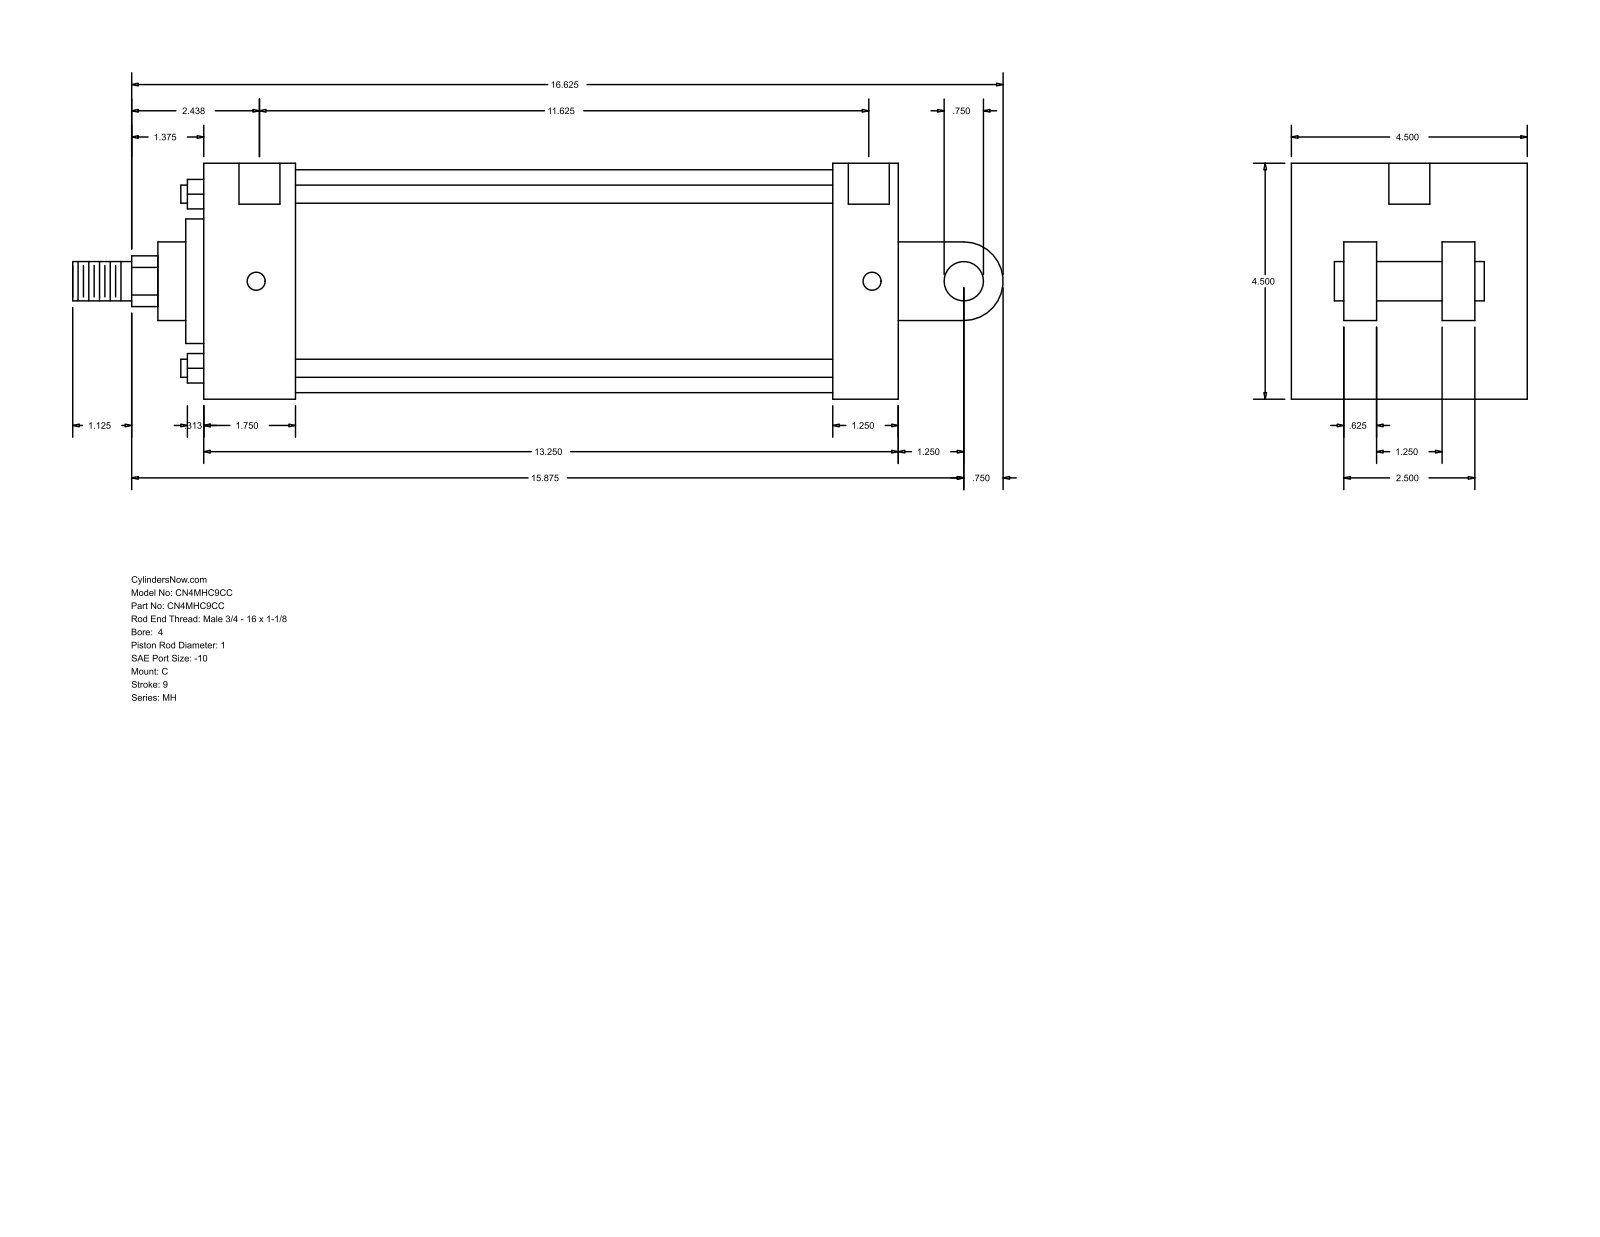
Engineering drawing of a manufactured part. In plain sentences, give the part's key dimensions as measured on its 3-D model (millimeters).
The part is named "MH_C__0400_1". Its 3-D file was written by "GSSL Pune (CONFIG_CONTROL_DESIGN)". It is 0 solids with 101 faces: 71 planar, 30 cylindrical and 0 other. Overall it measures 450.85 by 114.3 by 114.3 millimeters. Round holes: 4 of diameter 8.73, 2 of diameter 19.84. Round bosses or shafts: 4 of diameter 8.76, 2 of diameter 19.05, 1 of diameter 107.95, 1 of diameter 60.33, 1 of diameter 38.1, 1 of diameter 25.4. Partial cylindrical surfaces (rounded edges, fillets, slot ends): 1 of radius 12.29, 1 of radius 19.05. The main face-to-face distances are 114.3, 336.56, 44.46, 304.81, 260.35, 292.1, 31.75, 73.03, 41.27, 38.1. The hole center spacings are 1.58, 296.86, 298.44, 295.28.
